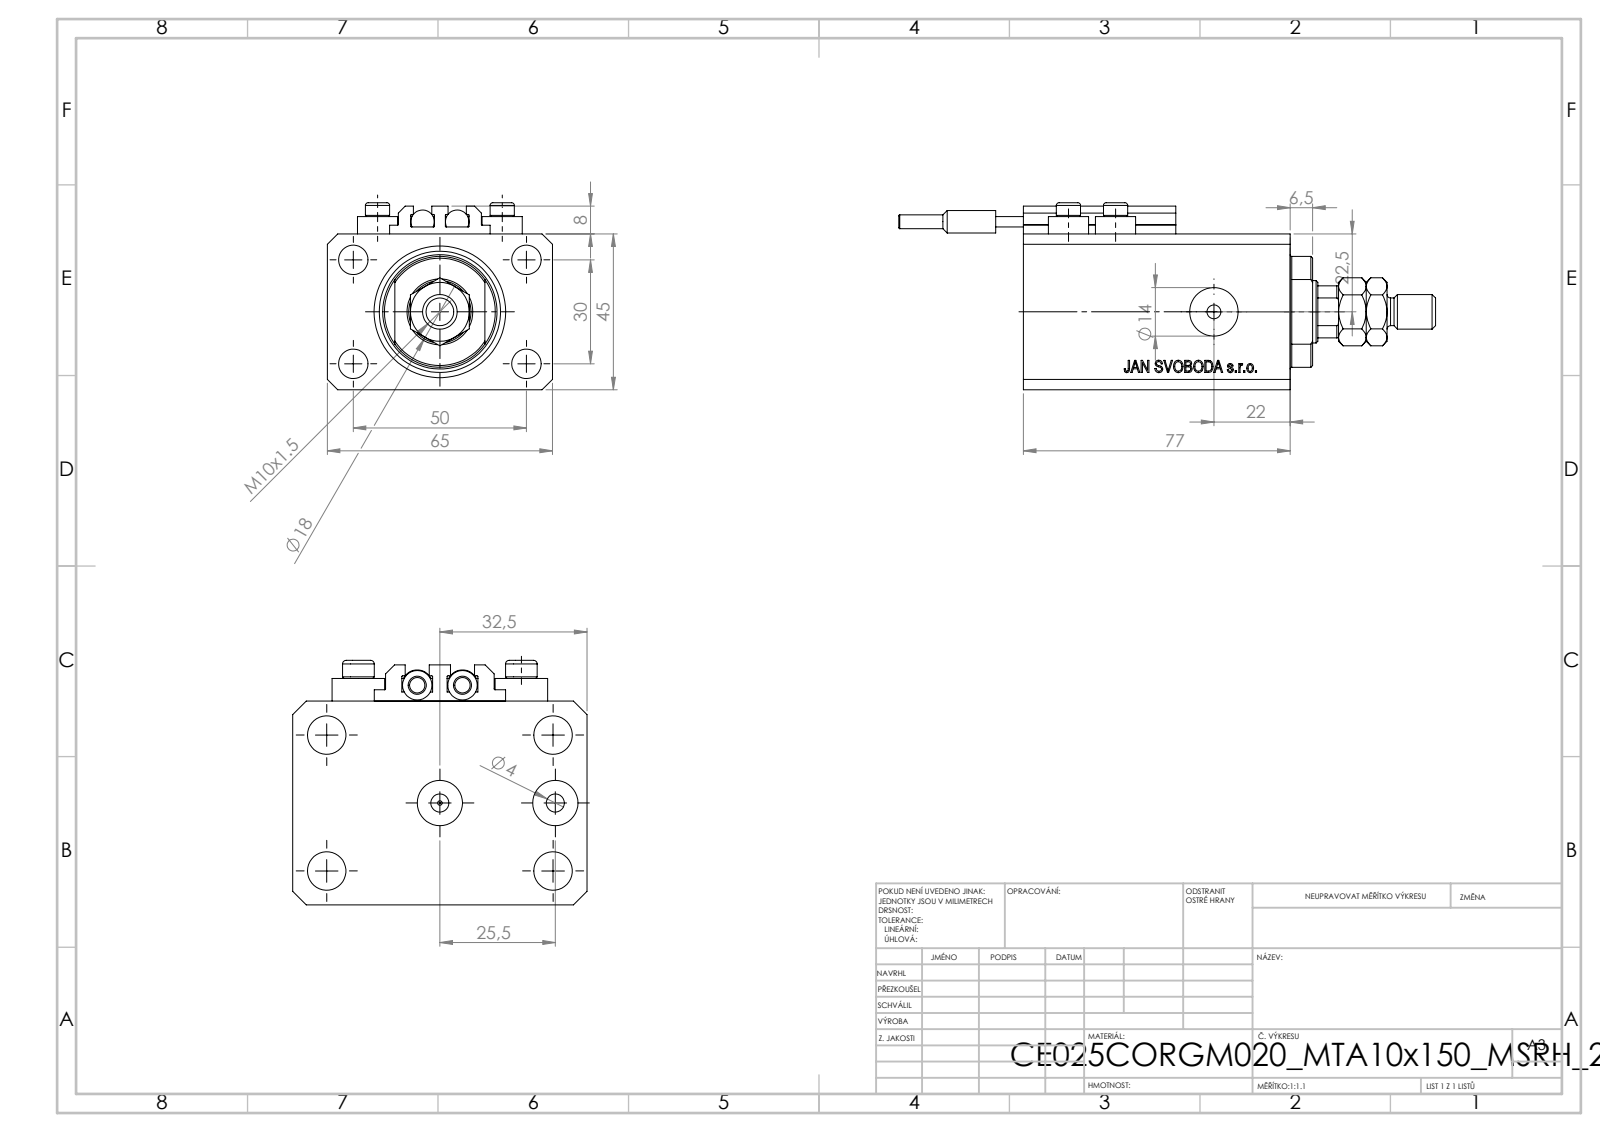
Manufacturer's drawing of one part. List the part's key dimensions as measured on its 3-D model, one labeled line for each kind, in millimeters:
Part name (STEP PRODUCT): V250CE_C_Body; V250CE_C_VCP; V250CE_VC_C; SWITCH_V250CE (+2 more)
STEP written by: SolidWorks 2019 (CONFIG_CONTROL_DESIGN)
Units: millimetres
Bodies: 11 solids, 1143 faces (551 planar, 108 cylindrical, 484 other)
Overall size (bounding box): 155 × 65 × 54
Volume: 219 560 mm³ · Surface area: 62 168 mm²
Round holes (diameter × count): ⌀4 ×8, ⌀8.5 ×5, ⌀10 ×2, ⌀14 ×2, ⌀1.25 ×1, ⌀18 ×1, ⌀25 ×1, ⌀38 ×1
Round bosses / shafts (diameter × count): ⌀11.6 ×4, ⌀7 ×4, ⌀6.8 ×2, ⌀6.5 ×2, ⌀4 ×2, ⌀8 ×1
Partial cylindrical surfaces — rounded edges, fillets, slot ends (radius × count): R0.2 ×10, R8.5 ×1, R16 ×1
Main face-to-face distances: 45, 65, 14, 77, 63, 6.9, 3, 47, 56.1, 70.1
Hole centre spacings: 29.15, 13.6, 15.01, 30, 36, 38.48, 50, 52.68
